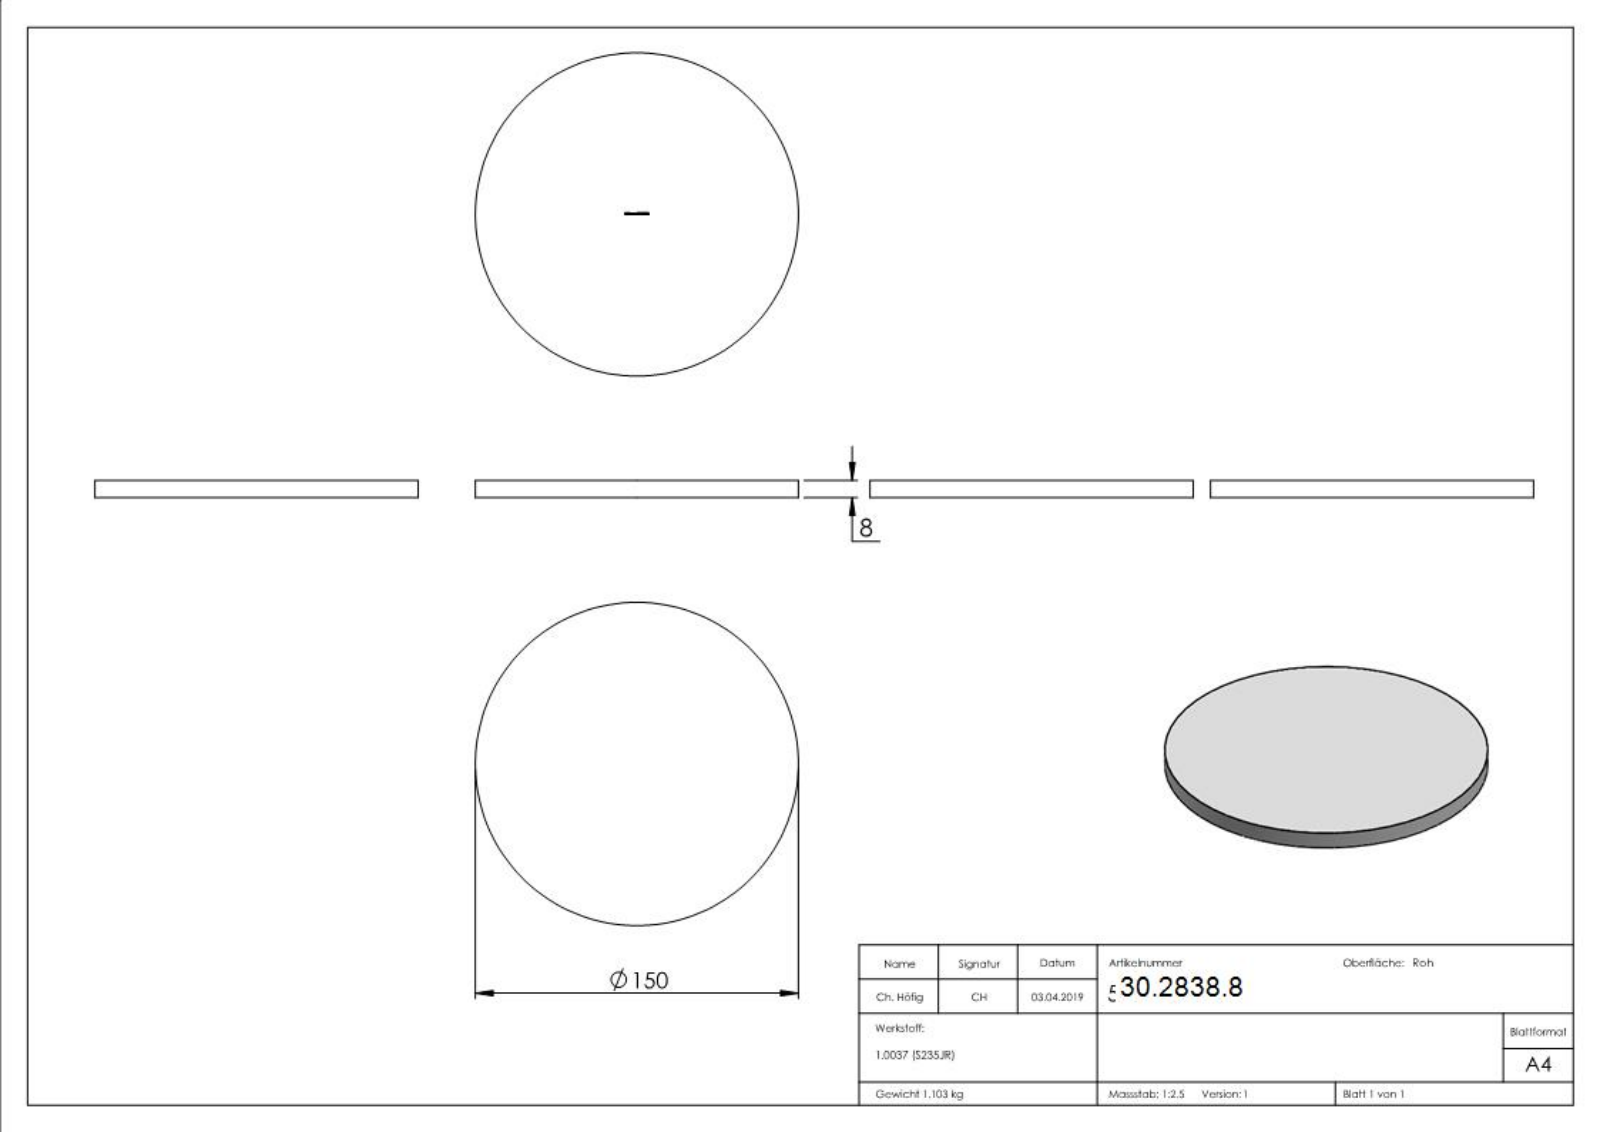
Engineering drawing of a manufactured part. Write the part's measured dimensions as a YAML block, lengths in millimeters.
part_name: "53150-ST-8"
step_written_by: "SolidWorks 2015 (CONFIG_CONTROL_DESIGN)"
units: millimeters
bodies: {solids: 1, faces: 240, planar: 119, cylindrical: 2, other: 119}
overall_size: [150, 150, 8]
volume: 141371
surface_area: 39119
round_bosses_or_shafts:
  - {diameter: 150, count: 1}
face_to_face_distances: [8, 7.9, 1.78, 0.44, 0.83, 0.76, 0.79, 0.99, 5.83, 1.21]
